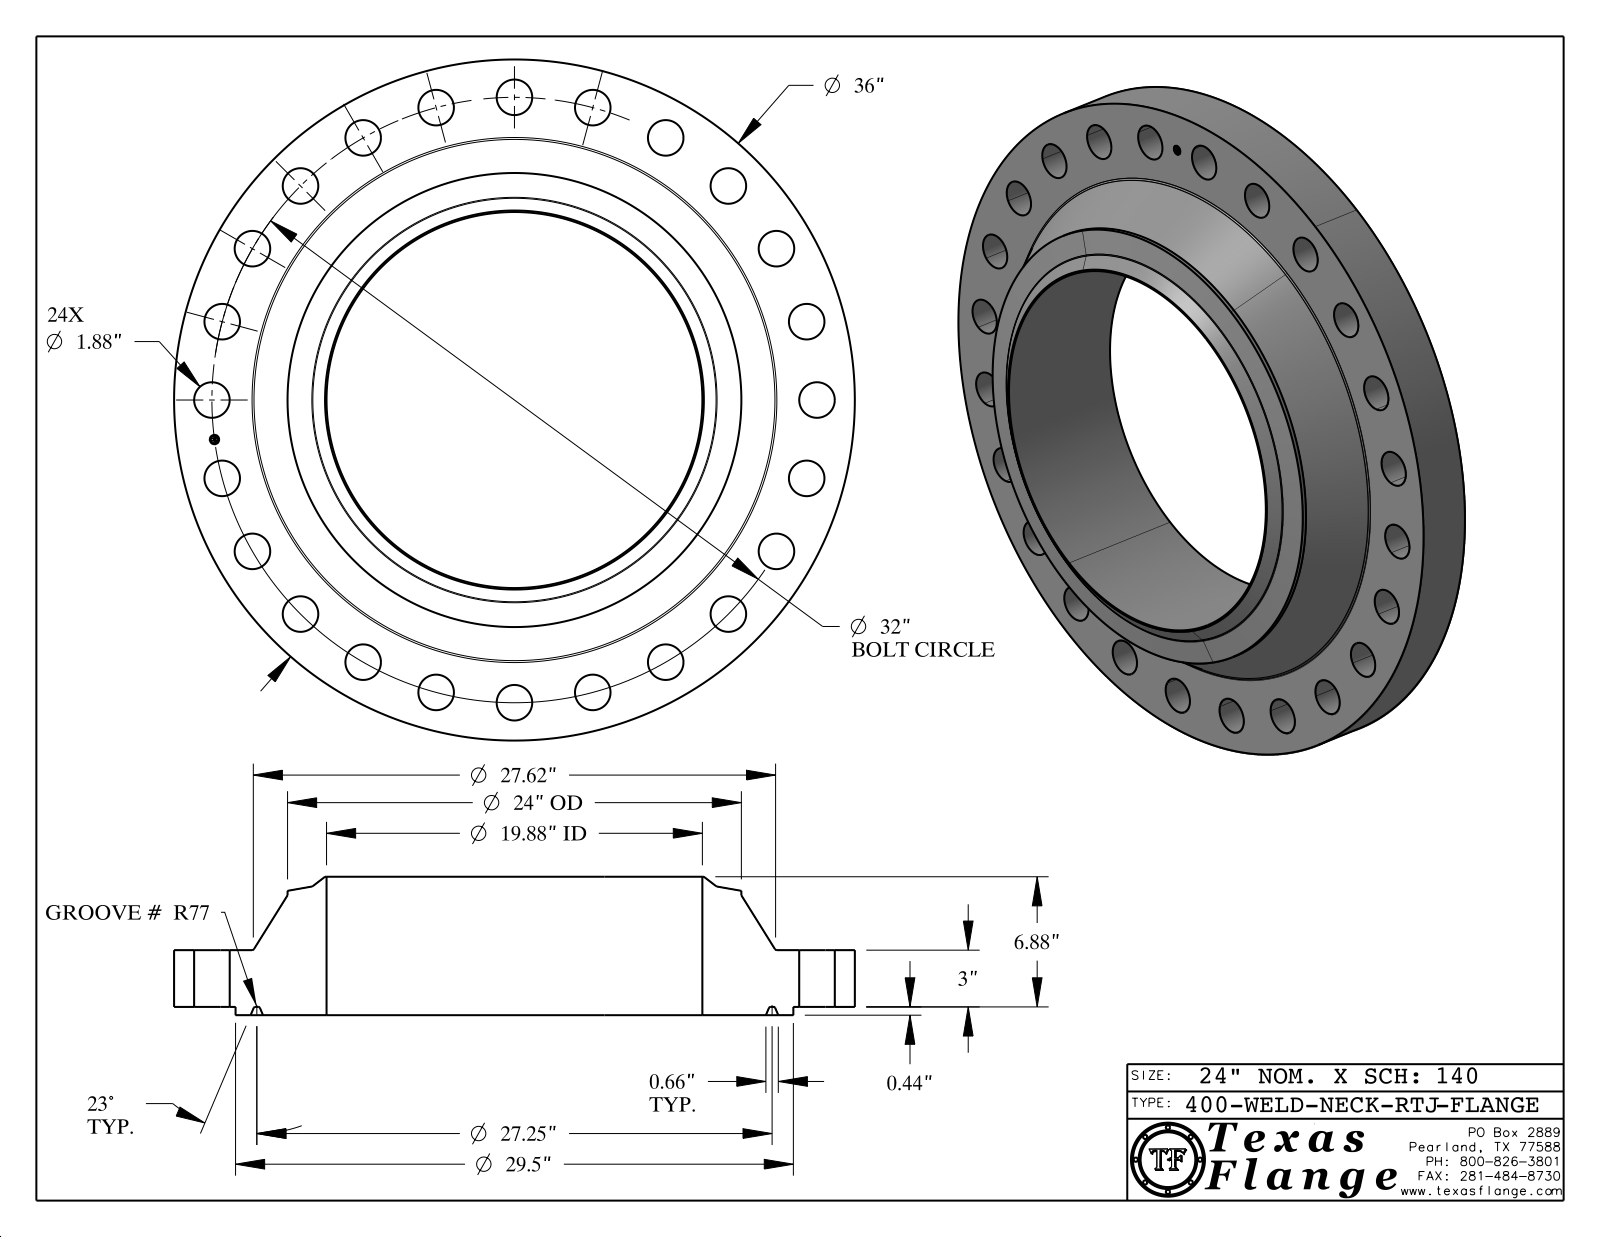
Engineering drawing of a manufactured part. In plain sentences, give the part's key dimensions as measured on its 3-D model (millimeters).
The part is named "400-WELD-NECK-RTJ". Its 3-D file was written by "CATIA V5 STEP AP214 (AUTOMOTIVE_DESIGN)". It is 1 solid with 465 faces: 371 planar, 76 cylindrical and 18 other. Overall it measures 914.4 by 914.4 by 185.9 millimeters. Its volume is 45 200 000 cubic millimeters and its surface area 1 775 000 square millimeters. Round holes: 24 of diameter 47.8, 1 of diameter 12.6, 1 of diameter 504.9. Round bosses or shafts: 8 of diameter 0.8, 1 of diameter 914.4, 1 of diameter 749.3, 1 of diameter 609.6, 1 of diameter 9.9. The main face-to-face distances are 87.3, 11.1, 76.2, 185.9, 174.8, 98.6, 86.9, 75.8, 0.4, 98.9. The hole center spacings are 406.4, 785.1, 106.1, 210.4, 311, 494.8, 574.7, 644.8.
